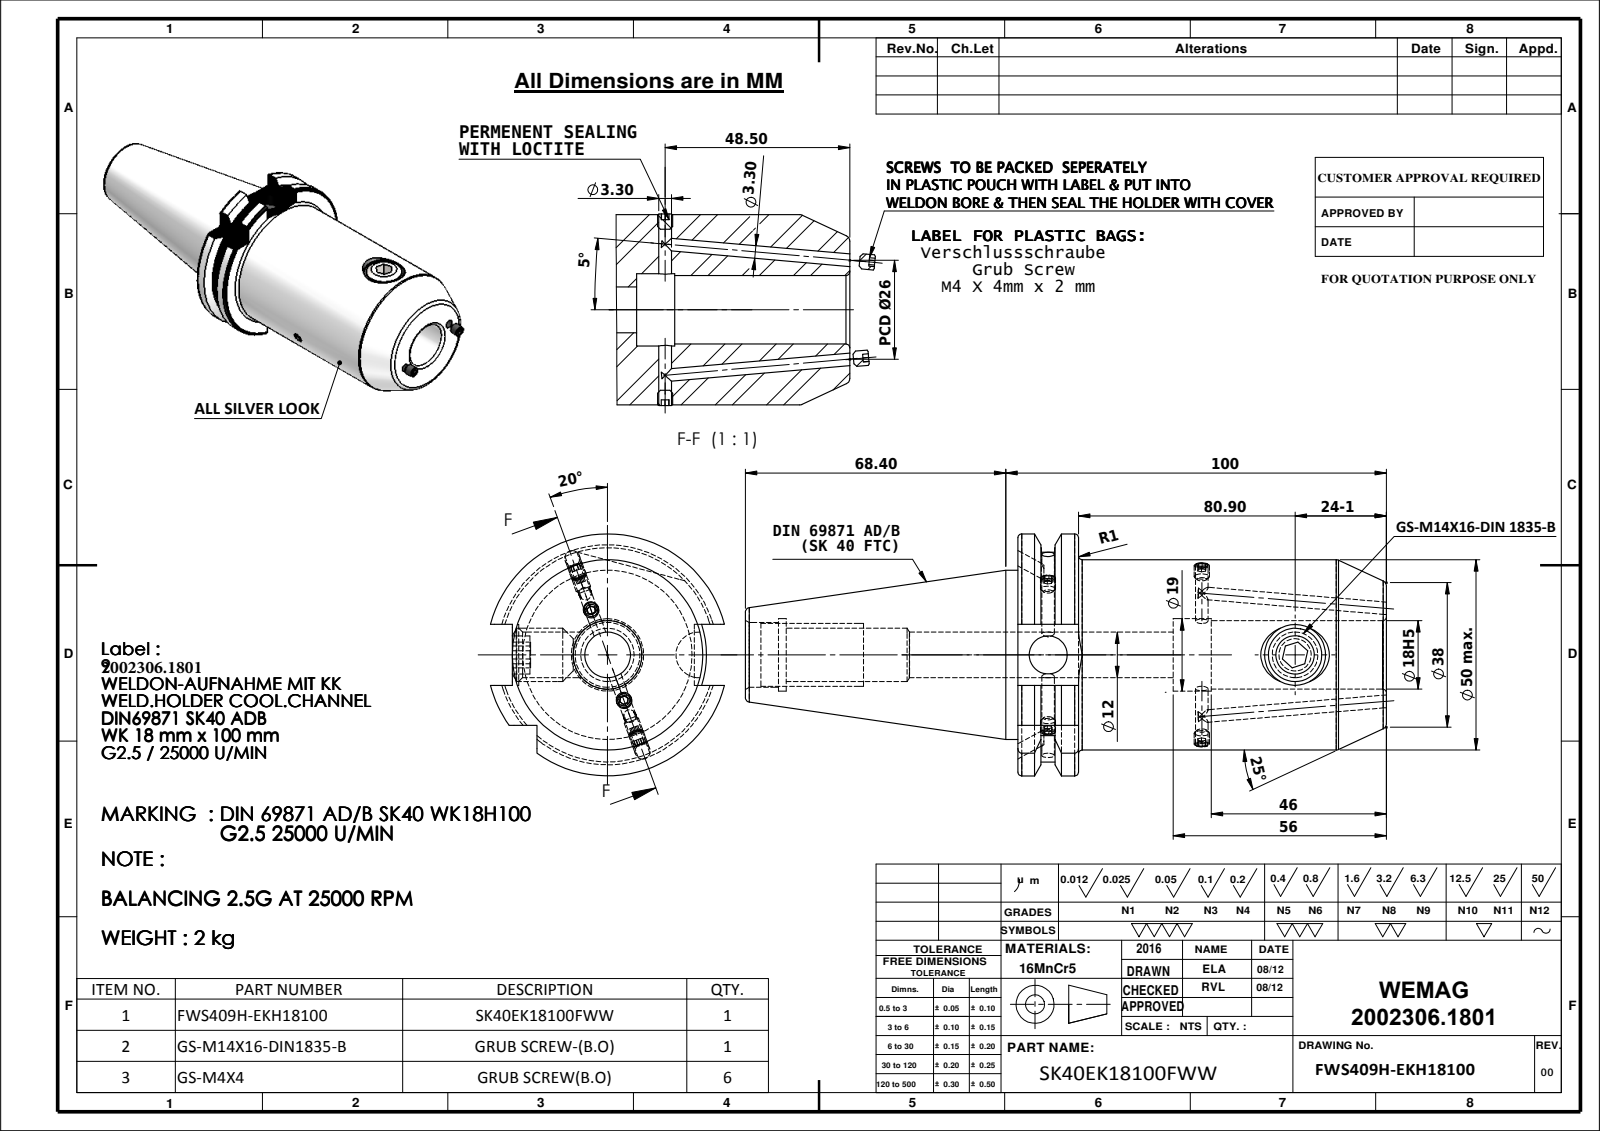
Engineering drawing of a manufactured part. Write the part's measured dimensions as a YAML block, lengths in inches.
part_name: "SK40EK18100FWW; M14X16_ISO 4026 - M12 x 12-N; 91406-WK218100; Copy of M4X4_DIN 913 - M4 x 4-N (+1 more)"
step_written_by: "SolidWorks 2009 (CONFIG_CONTROL_DESIGN)"
units: inches
bodies: {solids: 8, faces: 239, planar: 100, cylindrical: 66, other: 73}
overall_size: [6.894, 2.502, 2.42]
volume: 14.33
surface_area: 62.39
round_holes:
  - {diameter: 0.13, count: 5}
  - {diameter: 0.472, count: 2}
  - {diameter: 0.394, count: 1}
  - {diameter: 0.551, count: 1}
  - {diameter: 0.63, count: 1}
  - {diameter: 0.669, count: 1}
  - {diameter: 0.709, count: 1}
  - {diameter: 0.748, count: 1}
round_bosses_or_shafts:
  - {diameter: 0.157, count: 6}
  - {diameter: 1.969, count: 1}
  - {diameter: 1.75, count: 1}
  - {diameter: 0.551, count: 1}
partial_cylinders:
  - {radius: 1.107, count: 1}
  - {radius: 1.251, count: 1}
face_to_face_distances: [0.626, 3.811, 3.185, 1.882, 0.634, 1.606, 0.98, 2.205, 2.819, 3.445]
hole_center_spacings: [1.591, 2.553]
